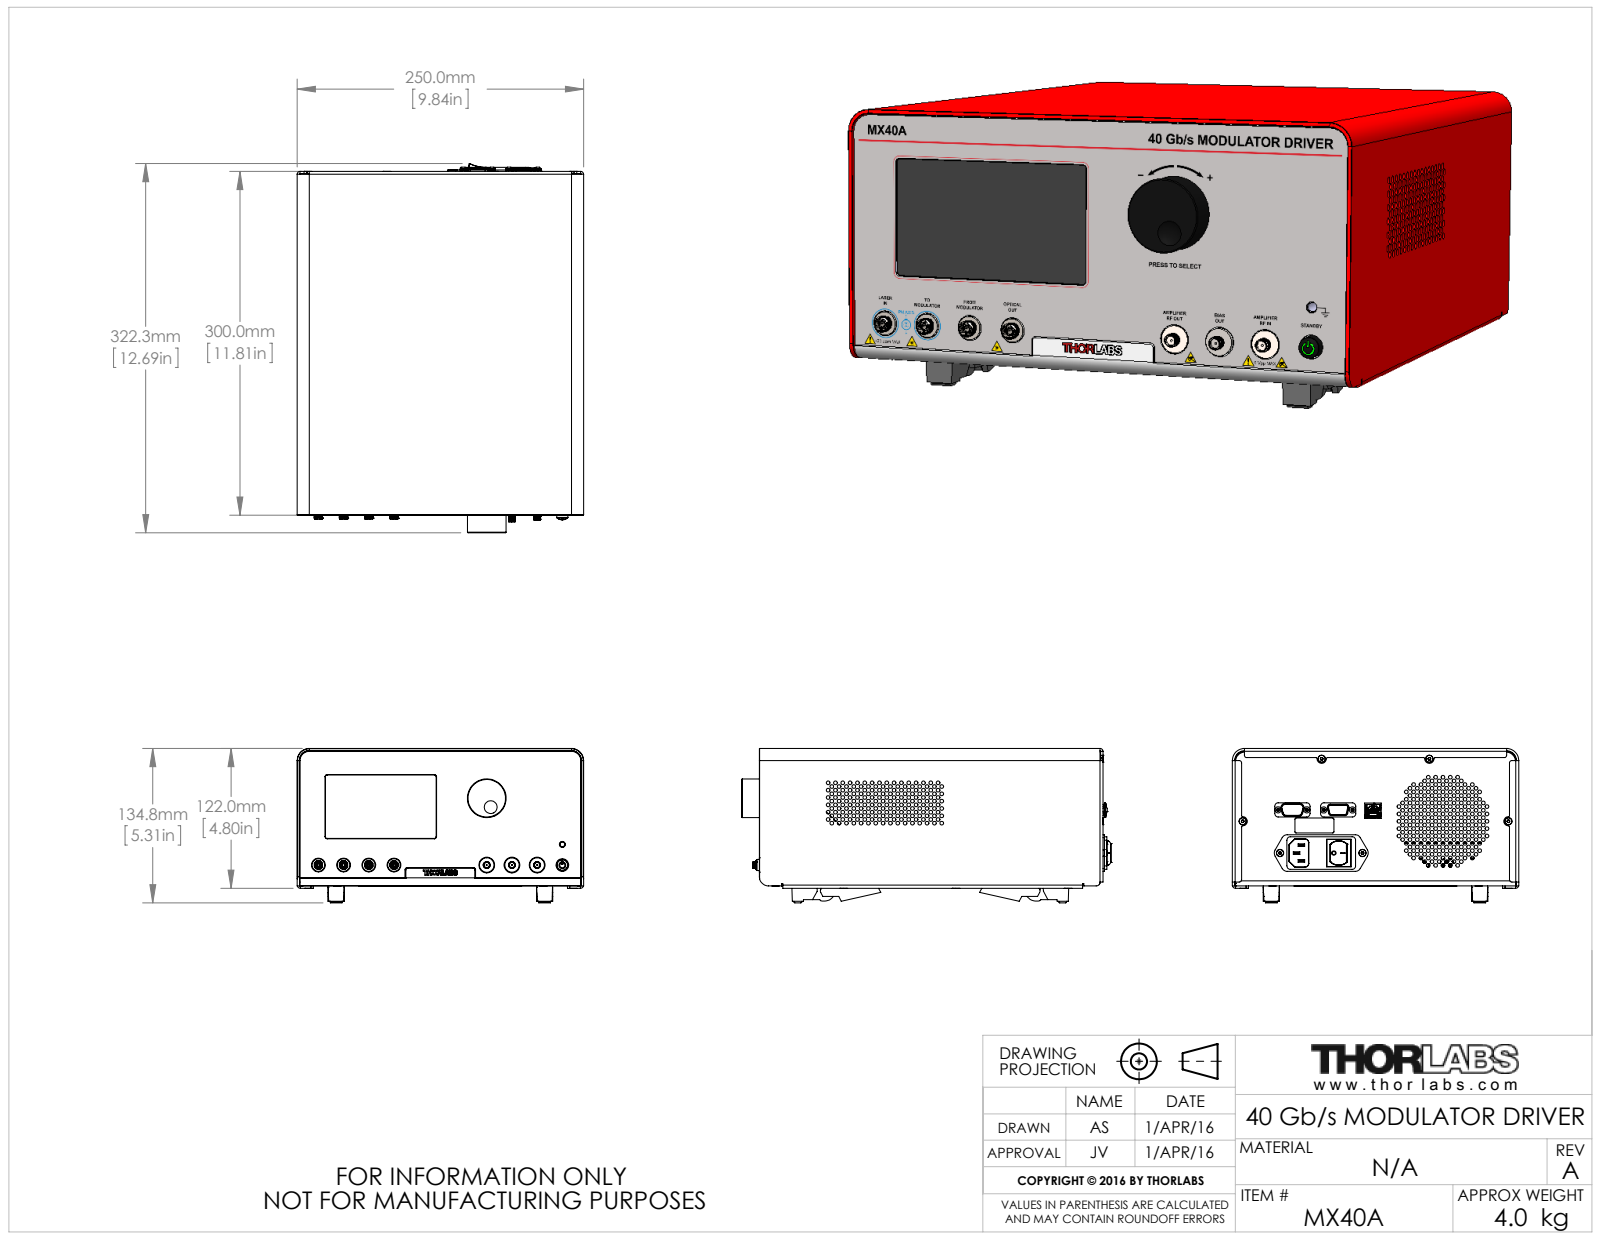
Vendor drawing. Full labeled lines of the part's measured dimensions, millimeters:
Part name (STEP PRODUCT): EHW-00003; EHW-00004; FAS-00062; OHW-00011 (+8 more)
STEP written by: SolidWorks 2014 (AUTOMOTIVE_DESIGN)
Units: millimetres
Bodies: 188 solids, 11703 faces (3529 planar, 6012 cylindrical, 2162 other)
Overall size (bounding box): 322.34 × 250 × 134.82
Volume: 787 534 mm³ · Surface area: 788 740 mm²
Round holes (diameter × count): ⌀2 ×482, ⌀3.2 ×459, ⌀2.46 ×37, ⌀3.4 ×28, ⌀4.37 ×25, ⌀0.92 ×15, ⌀1.66 ×15, ⌀3.6 ×8, ⌀4.37 ×8, ⌀2.6 ×5, ⌀2.5 ×4, ⌀3.15 ×4
Round bosses / shafts (diameter × count): ⌀3 ×39, ⌀4.35 ×33, ⌀3.48 ×33, ⌀6 ×29, ⌀2.35 ×28, ⌀3.91 ×11, ⌀1.02 ×9, ⌀4 ×6
Partial cylindrical surfaces — rounded edges, fillets, slot ends (radius × count): R2 ×71, R0.5 ×46, R1 ×38, R0.25 ×26, R0.15 ×24, R3 ×24, R0.2 ×19, R0.3 ×19
Main face-to-face distances: 2, 118, 120, 116, 248, 4.75, 243.25, 2.75, 245.25, 293.65
Hole centre spacings: 14.31, 6.4, 4.24, 9.05, 8.48, 12.72, 12.8, 16.96
